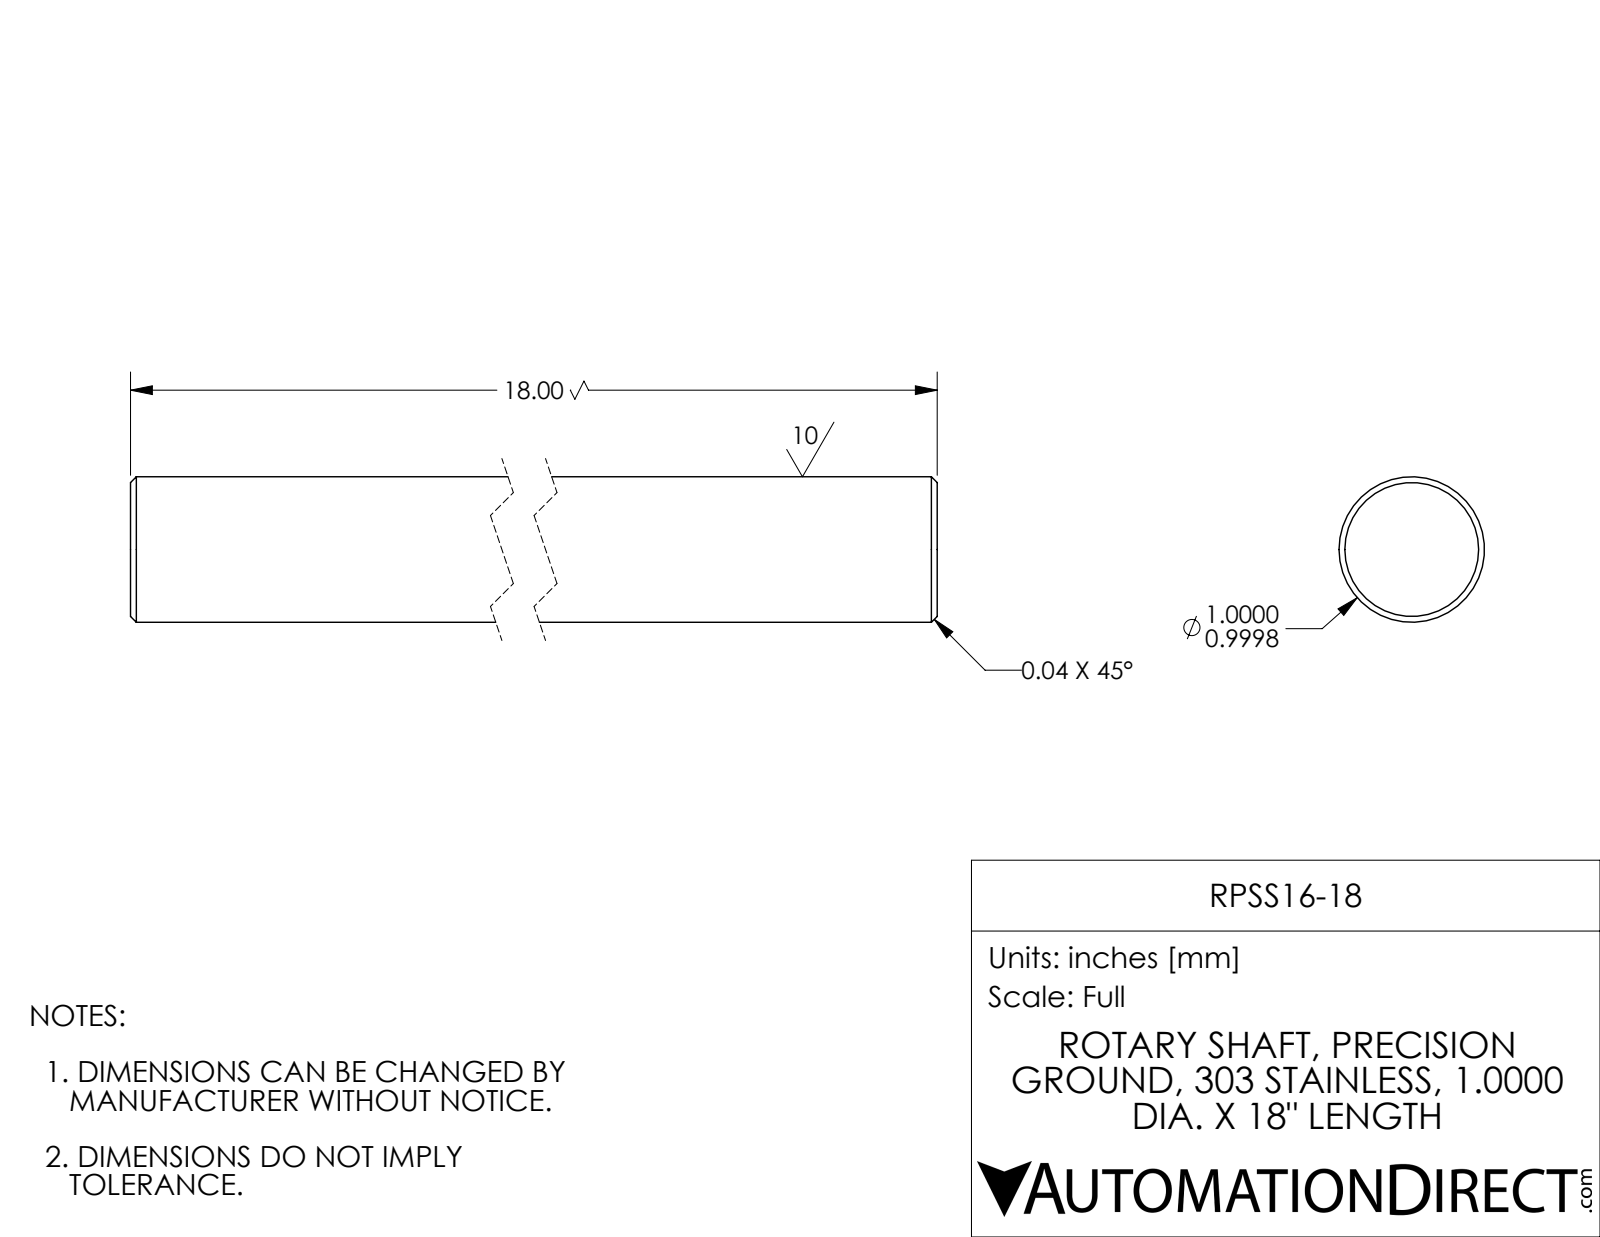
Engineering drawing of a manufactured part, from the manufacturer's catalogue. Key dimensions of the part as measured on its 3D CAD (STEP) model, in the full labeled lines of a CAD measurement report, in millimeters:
Part name (STEP PRODUCT): RPSS16-18
STEP written by: SolidWorks 2017 (AUTOMOTIVE_DESIGN)
Units: millimetres
Bodies: 1 solid, 8 faces (2 planar, 2 cylindrical, 4 other)
Overall size (bounding box): 457.2 × 25.4 × 25.4
Volume: 231 500 mm³ · Surface area: 37 400 mm²
Round bosses / shafts (diameter × count): ⌀25.4 ×1
Main face-to-face distances: 457.2
